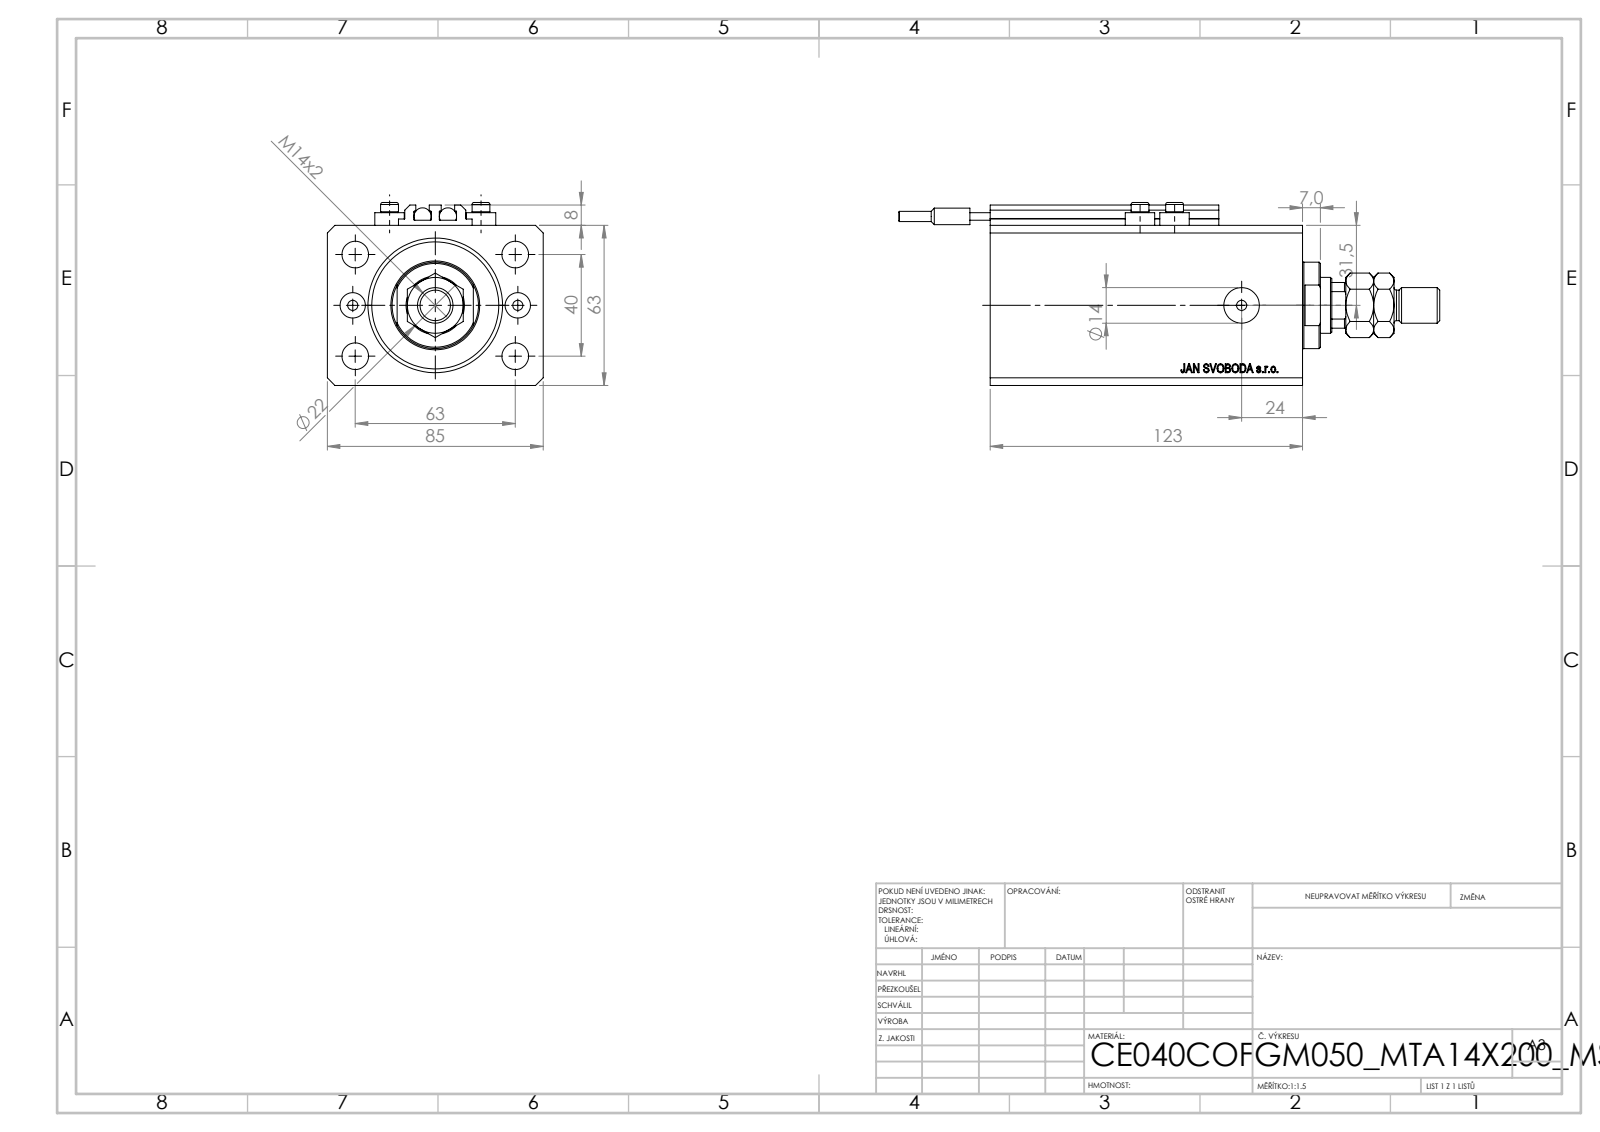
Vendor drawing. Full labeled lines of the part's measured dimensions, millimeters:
Part name (STEP PRODUCT): ALLEN BOLT V250CE; V250CE_C_Body; MTA; V250CE_C_VCP (+2 more)
STEP written by: SolidWorks 2019 (CONFIG_CONTROL_DESIGN)
Units: millimetres
Bodies: 11 solids, 1135 faces (551 planar, 102 cylindrical, 482 other)
Overall size (bounding box): 213 × 85 × 72
Volume: 601 456 mm³ · Surface area: 119 480 mm²
Round holes (diameter × count): ⌀4 ×8, ⌀10.5 ×4, ⌀10 ×2, ⌀14 ×2, ⌀12.5 ×1, ⌀22 ×1, ⌀40 ×1, ⌀53 ×1
Round bosses / shafts (diameter × count): ⌀11.6 ×4, ⌀7 ×4, ⌀6.8 ×2, ⌀6.5 ×2, ⌀4 ×2, ⌀34 ×1, ⌀14 ×1, ⌀12 ×1
Partial cylindrical surfaces — rounded edges, fillets, slot ends (radius × count): R0.2 ×10, R10.5 ×1
Main face-to-face distances: 63, 85, 123, 17, 106, 11.4, 94.6, 111.6, 3, 10
Hole centre spacings: 20.02, 37.31, 67.05, 13.6, 32.5, 36, 38.48, 40
